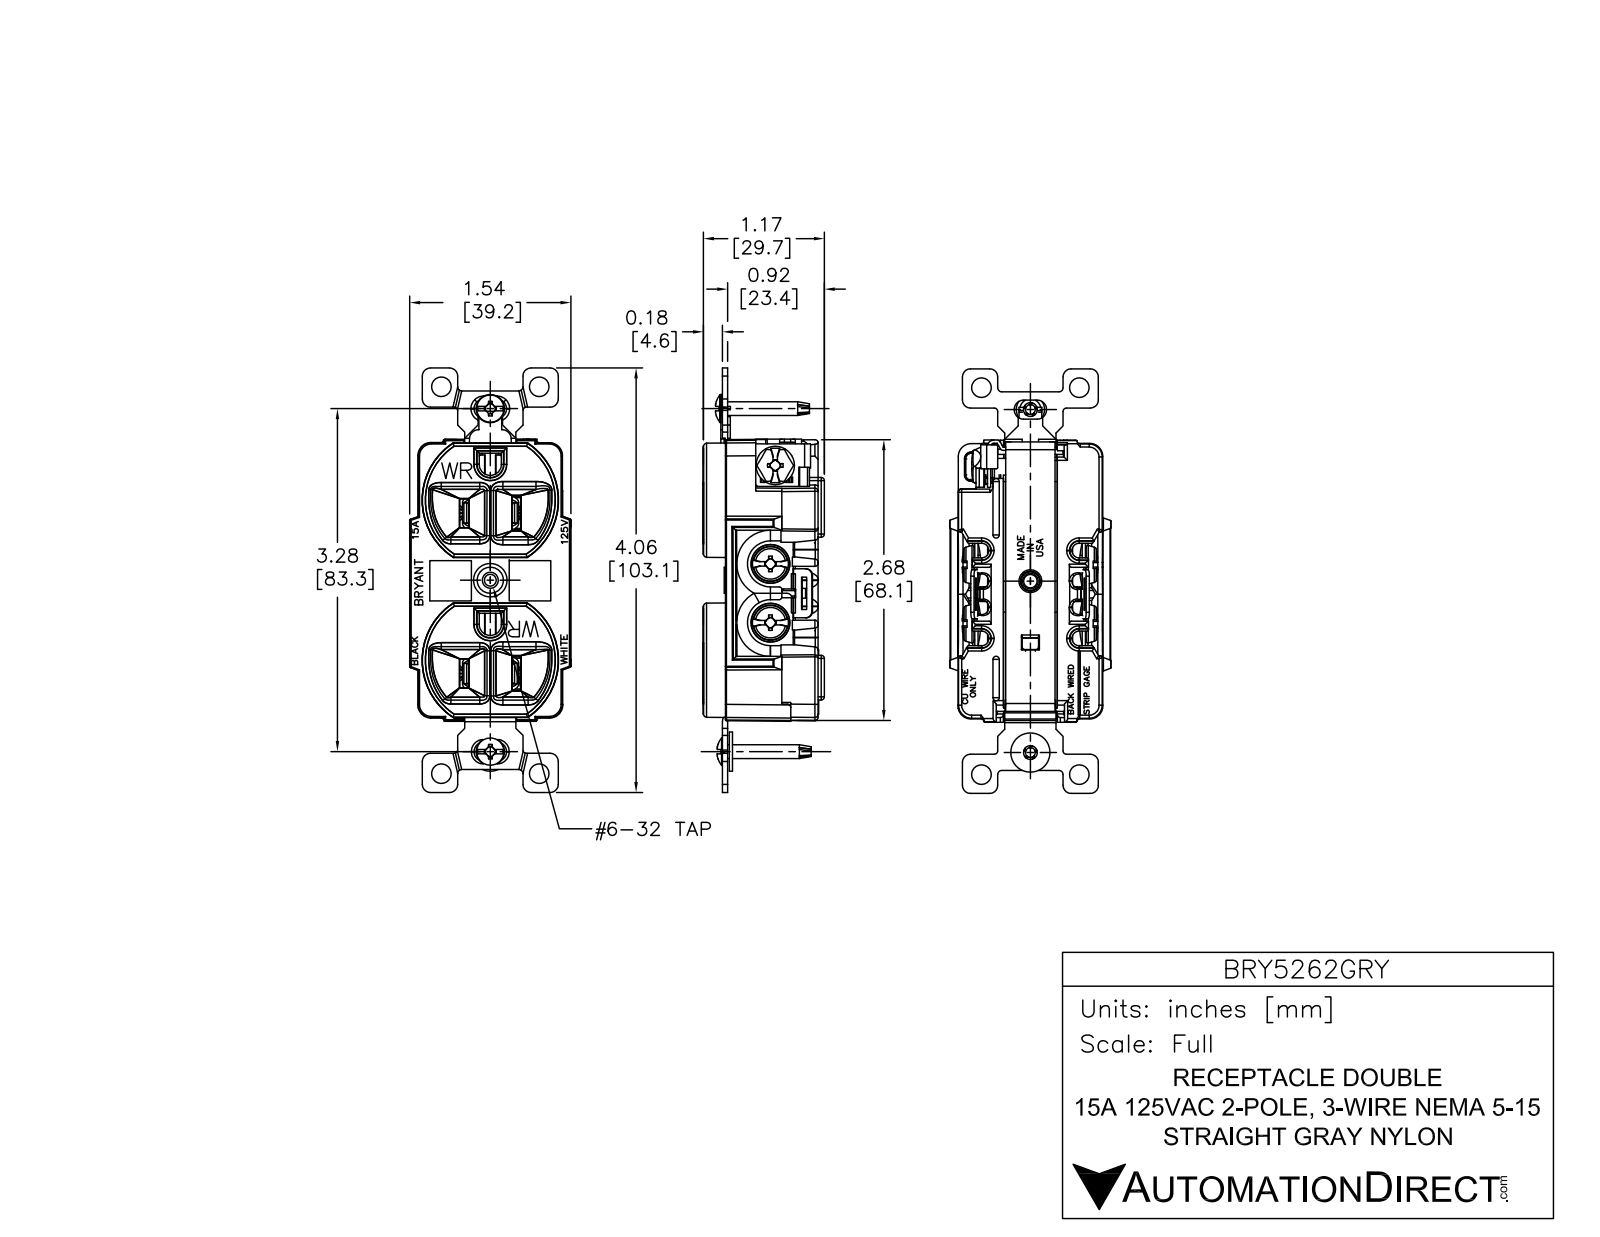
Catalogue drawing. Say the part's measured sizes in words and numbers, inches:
The part is named "BRY5262GRY". Its 3-D file was written by "SolidWorks 2013 (AUTOMOTIVE_DESIGN)". It is 1 solid with 569 faces: 304 planar, 214 cylindrical and 51 other. Overall it measures 4.025 by 1.5 by 1.105 inches. Its volume is 3.242 cubic inches and its surface area 24.48 square inches. Round holes: 4 of diameter 0.185, 1 of diameter 0.115, 1 of diameter 0.25. Round bosses or shafts: 2 of diameter 0.375, 2 of diameter 0.135, 1 of diameter 0.37, 1 of diameter 0.36. Partial cylindrical surfaces (rounded edges, fillets, slot ends): 26 of radius 0.1, 8 of radius 0.03, 8 of radius 0.075, 6 of radius 0.15, 2 of radius 0.06, 2 of radius 0.12, 2 of radius 0.65. The main face-to-face distances are 0.05, 0.24, 1.035, 0.07, 0.82, 0.89, 0.19, 0.5, 0.045, 0.865. The hole center spacings are 1.88, 0.925, 3.645, 3.761.
